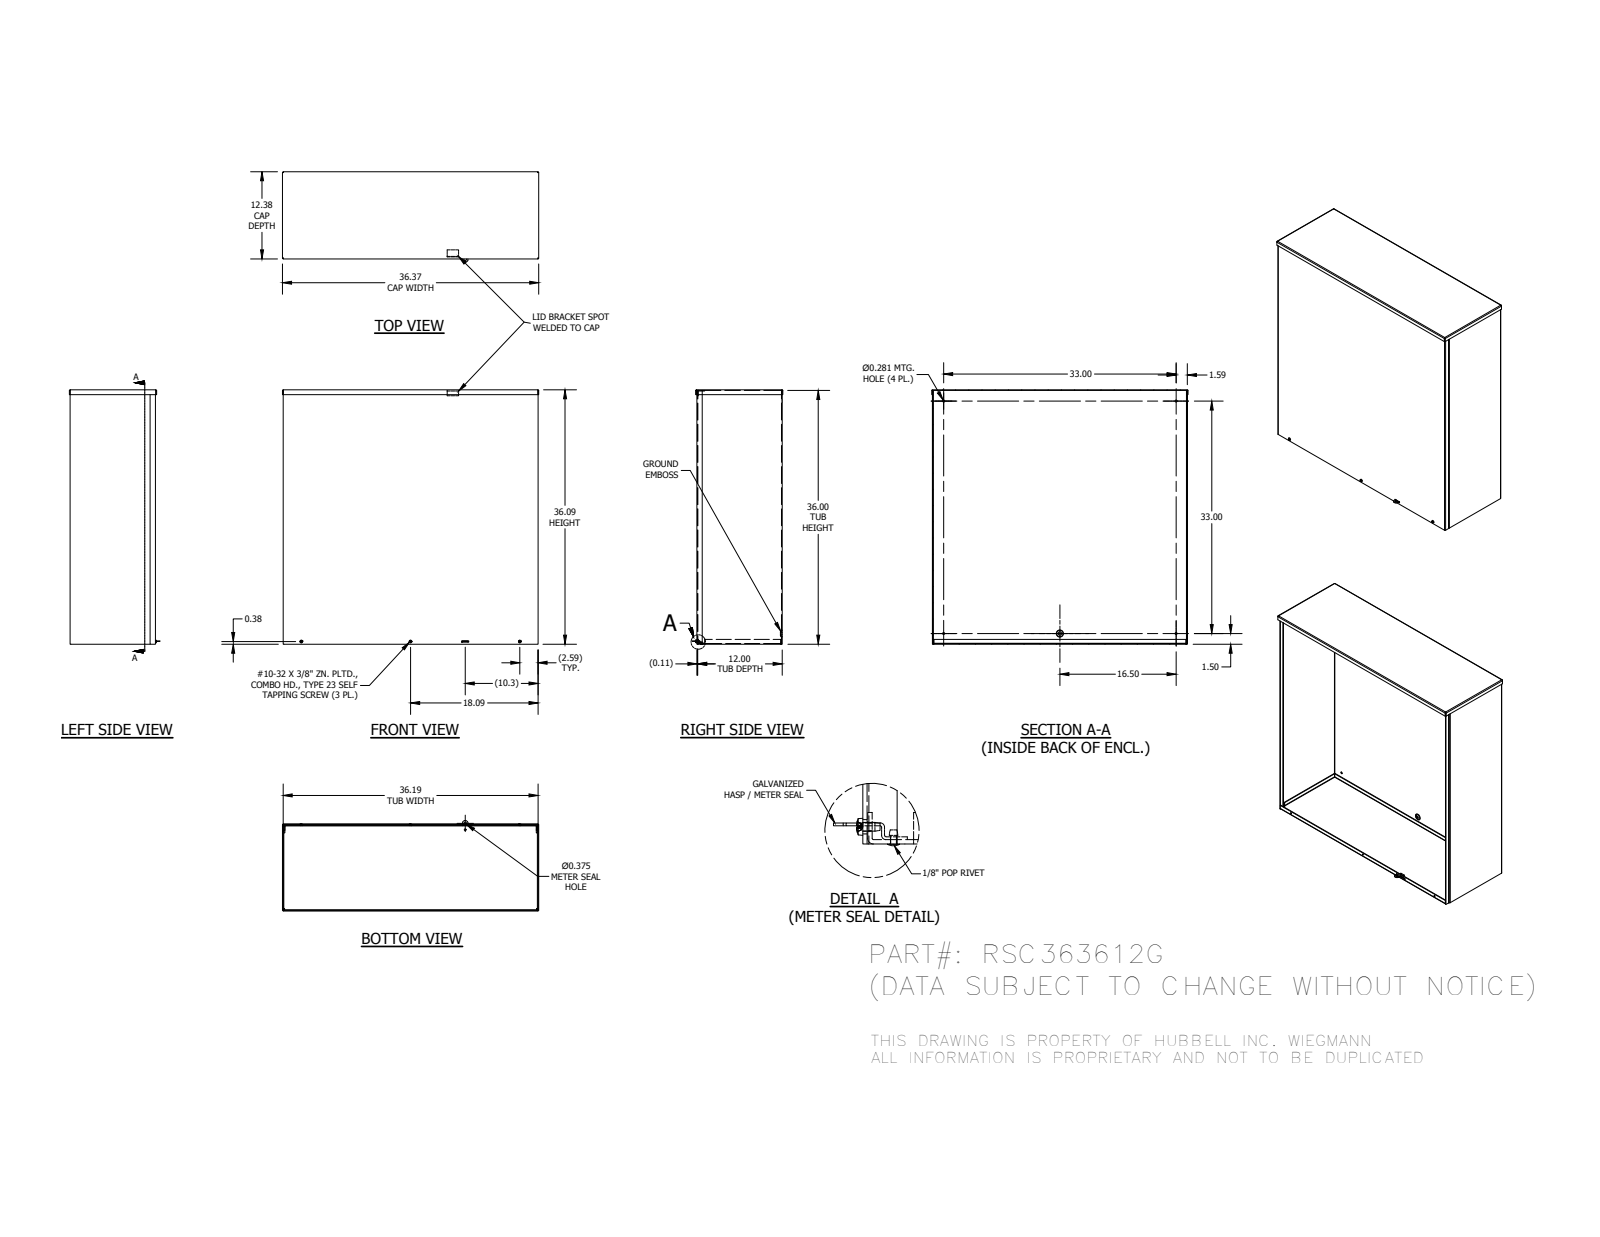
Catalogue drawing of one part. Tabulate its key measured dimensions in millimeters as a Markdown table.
| quantity | value |
| --- | --- |
| part name | RSC363612GBKPA; RSC3612GEWPA; RSC3636GLFA; RSC3612GCPA (+5 more) |
| STEP written by | Autodesk Inventor 2014 (AUTOMOTIVE_DESIGN) |
| units | millimeters |
| bodies | 11 solids, 367 faces (226 planar, 64 cylindrical, 77 other) |
| overall size | 923.92 × 917.8 × 326.24 |
| volume | 6 905 000 mm³ |
| surface area | 5 839 000 mm² |
| round holes (diameter × count) | 7.94 × 6, 4.34 × 4, 7.14 × 4, 3.17 × 1, 3.45 × 1, 9.52 × 1 |
| round bosses / shafts (diameter × count) | 4.83 × 3, 6.65 × 1, 3.17 × 1 |
| partial cylindrical surfaces (radius × count) | 0.79 × 19, 3.17 × 16, 2.37 × 2, 2.67 × 1, 10.16 × 1 |
| main face-to-face distances | 2.38, 305.2, 307.58, 302.82, 916.78, 914.4, 919.16, 912.02, 3.79, 912.99 |
| hole center spacings | 393.7, 978.09, 420.07, 813.3, 787.4, 38.24, 394.74, 838.2 |
